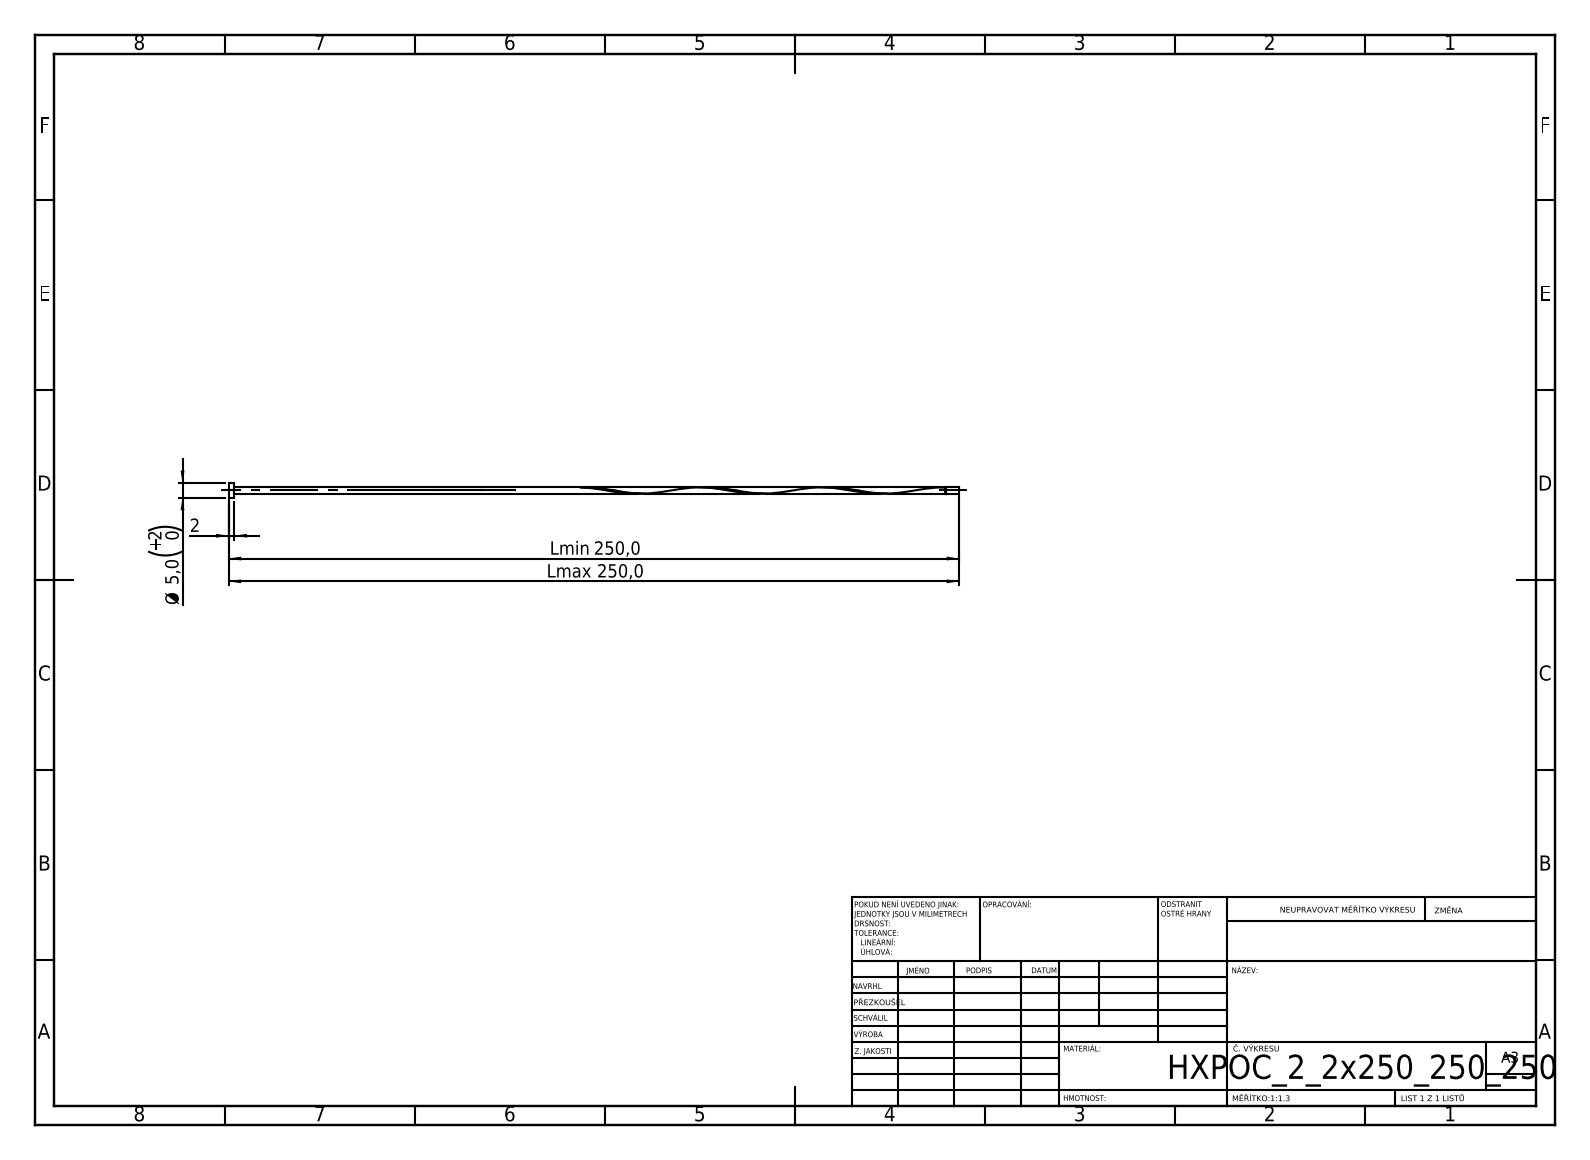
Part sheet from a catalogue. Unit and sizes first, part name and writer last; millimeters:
Units: millimetres
Overall size (bounding box): 250 × 5 × 5
Round bosses / shafts (diameter × count): ⌀5 ×1, ⌀2.2 ×1, ⌀1.76 ×1
Main face-to-face distances: 2, 250, 248, 245.65, 243.65, 4.35, 245.21, 243.21, 0.44, 4.79
Volume: 1 184 mm³ · Surface area: 2 390 mm²
Bodies: 1 solid, 16 faces (6 planar, 9 cylindrical, 1 other)
STEP written by: SolidWorks 2019 (CONFIG_CONTROL_DESIGN)
